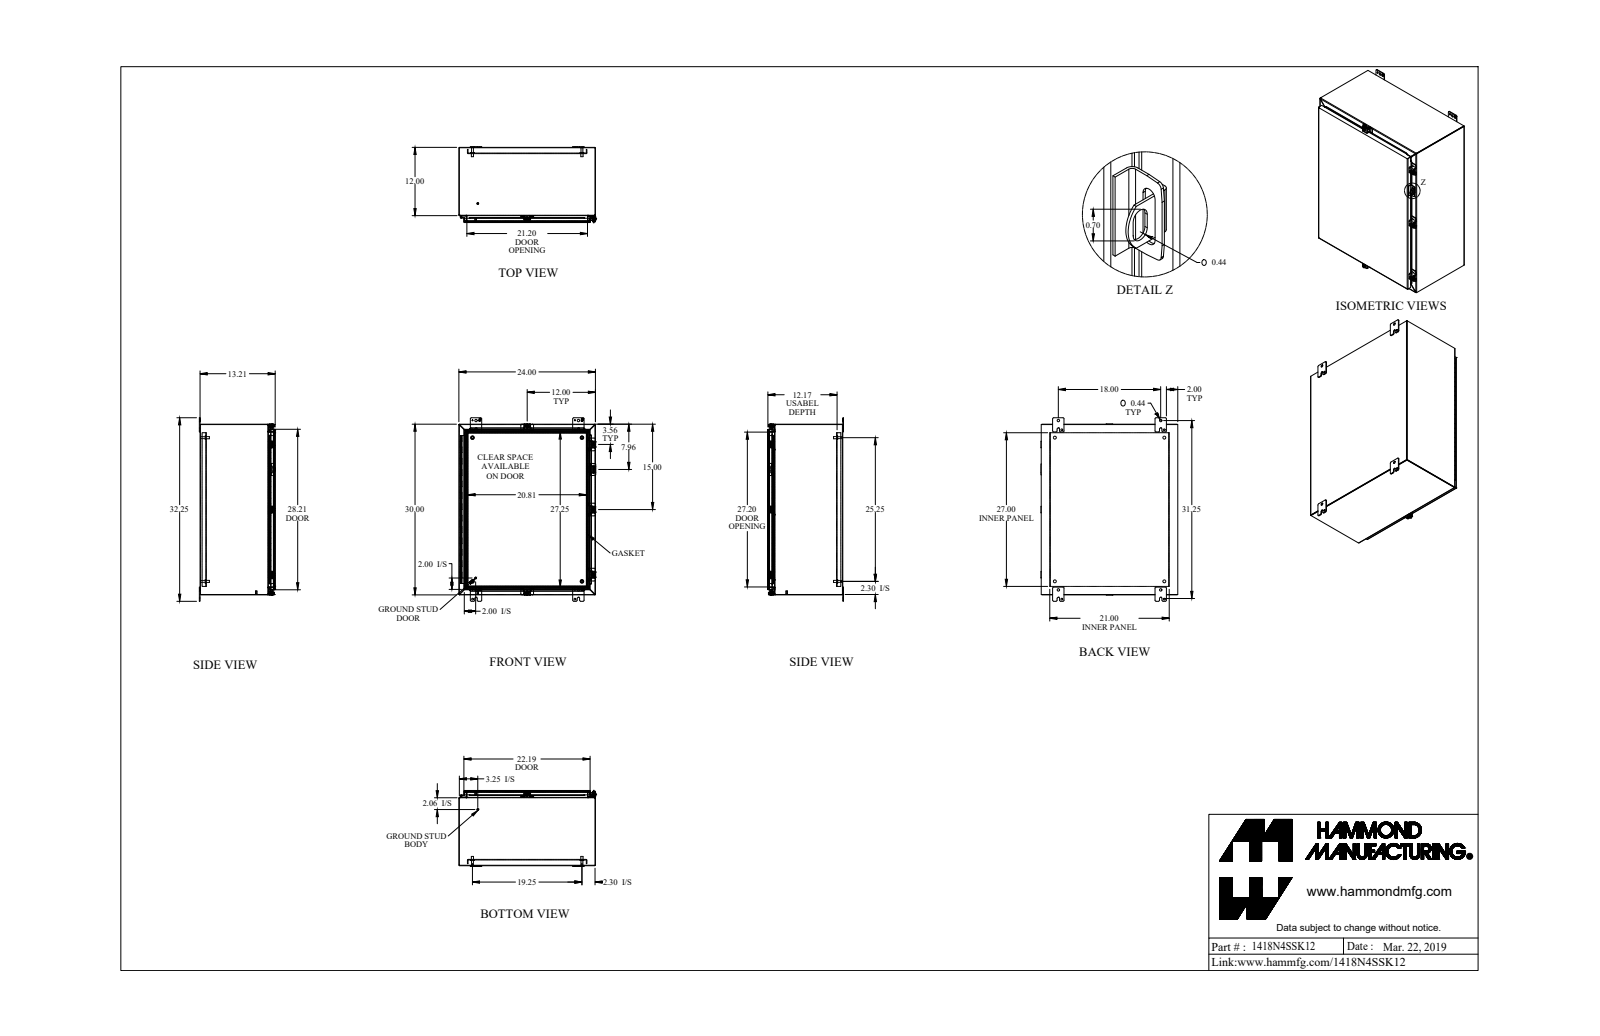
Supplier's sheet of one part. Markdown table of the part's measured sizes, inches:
| quantity | value |
| --- | --- |
| part name | 1418N4SSK12_Default |
| STEP written by | SolidWorks 2019 (CONFIG_CONTROL_DESIGN) |
| units | inches |
| bodies | 45 solids, 1651 faces (1013 planar, 552 cylindrical, 86 other) |
| overall size | 32.25 × 24.063 × 13.375 |
| volume | 289 in³ |
| surface area | 7 637 in² |
| round holes (diameter × count) | 0.213 × 5, 0.265 × 5, 0.375 × 5, 0.313 × 4, 0.437 × 4, 0.5 × 4, 0.307 × 2, 0.445 × 2, 0.125 × 1, 0.187 × 1 |
| round bosses / shafts (diameter × count) | 0.5 × 5, 0.39 × 5, 0.244 × 5, 0.65 × 4, 0.375 × 4, 0.332 × 4, 1 × 2, 0.313 × 2 |
| partial cylindrical surfaces (radius × count) | 0.25 × 28, 0.048 × 27, 0.143 × 27, 0.188 × 26, 0.036 × 22, 0.108 × 22, 0.125 × 10, 0.141 × 10 |
| main face-to-face distances | 0.072, 23.928, 0.072, 13.066, 13.138, 13.138, 13.21, 0.095, 0.937, 1.009 |
| hole center spacings | 29.018, 9.857, 18, 25.25, 31.751, 2.434, 3.065, 9.857 |
